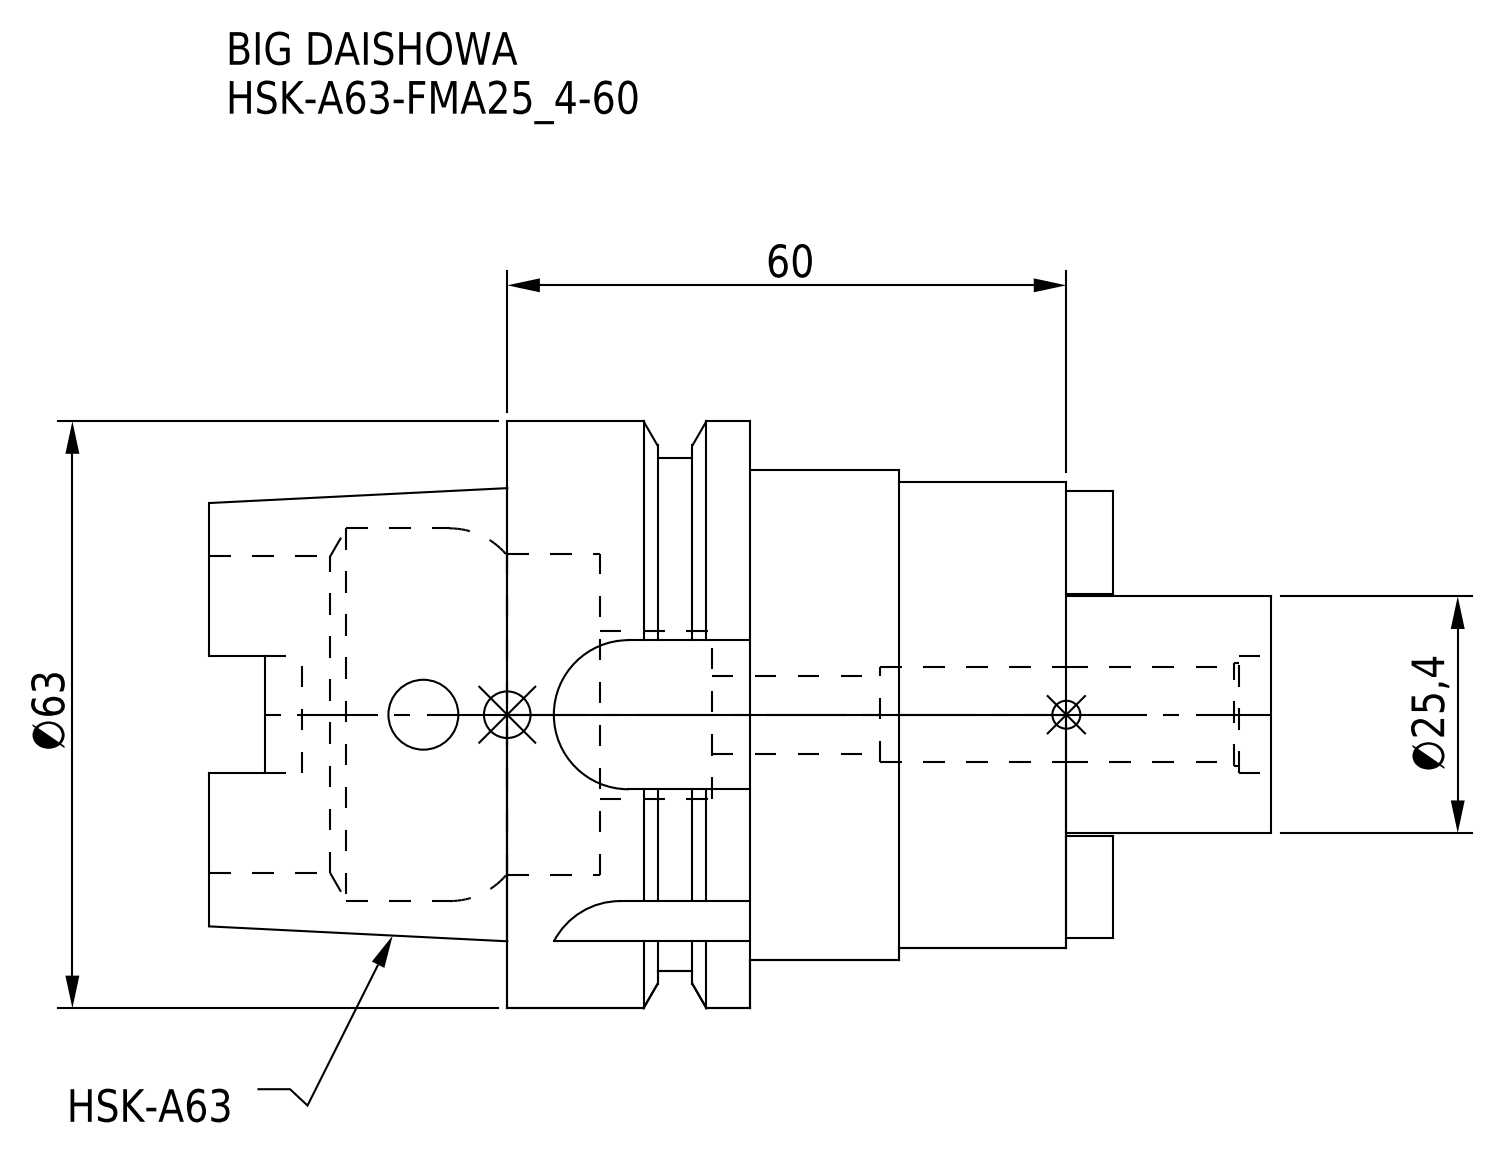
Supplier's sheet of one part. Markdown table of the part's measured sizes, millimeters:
| quantity | value |
| --- | --- |
| part name | HSK-A63-FMA25_4-60 |
| STEP written by | CREO PARAMETRIC BY PTC INC, 2016380 (AUTOMOTIVE_DESIGN) |
| units | millimeters |
| bodies | 1 solid, 98 faces (46 planar, 40 cylindrical, 12 other) |
| overall size | 114 × 63 × 63 |
| volume | 159 699 mm³ |
| surface area | 31 824 mm² |
| round holes (diameter × count) | 7.5 × 1, 8.4 × 1, 10.25 × 1, 11 × 1, 12.5 × 1, 18 × 1, 34 × 1, 34.5 × 1, 40 × 1 |
| round bosses / shafts (diameter × count) | 63 × 1, 55 × 1, 52.6 × 1, 50 × 1, 25.4 × 1 |
| partial cylindrical surfaces (radius × count) | 8 × 2, 9 × 1 |
| main face-to-face distances | 60, 26, 34, 50.05, 16.05, 9.95, 32, 92, 58, 41.95 |
